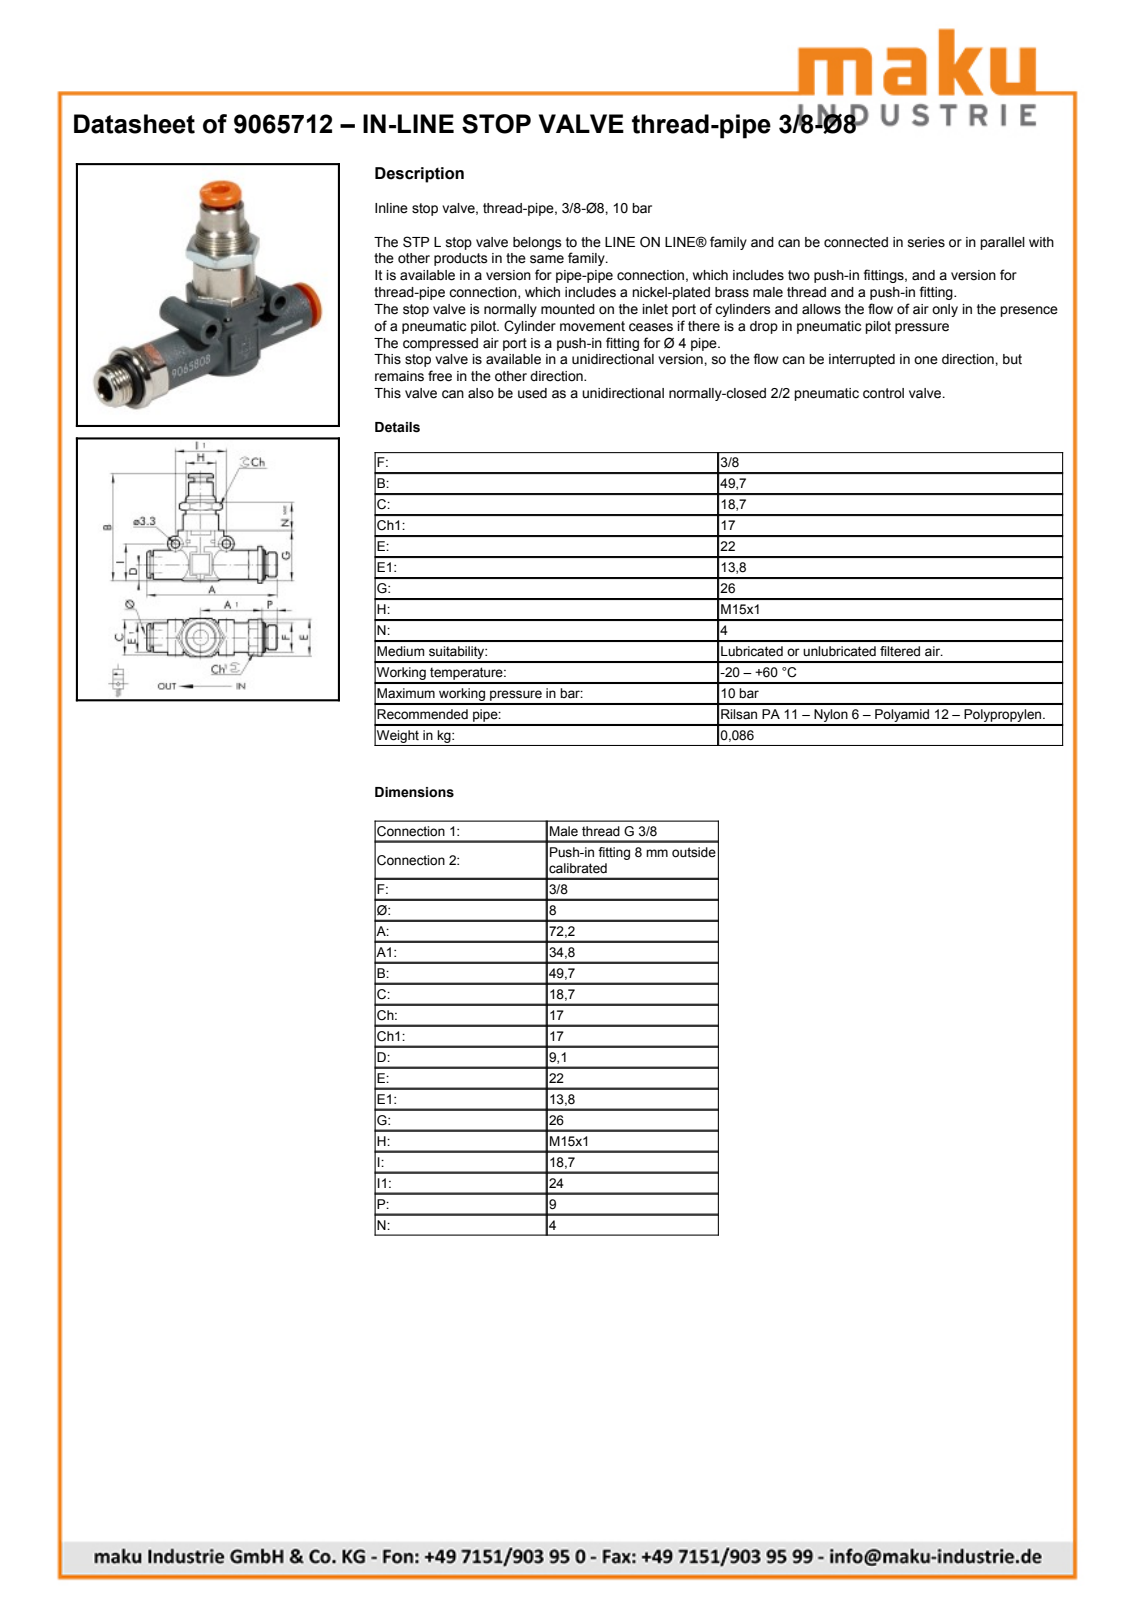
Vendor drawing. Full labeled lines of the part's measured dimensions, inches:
Part name (STEP PRODUCT): 9065712; LINE-ON-LINE D8 PNV_L-body; LINE-ON-LINE D8-3/8 RML-thread port; LINE-ON-LINE D8 VNR-L bushing (+2 more)
STEP written by: PARTsolutions (AUTOMOTIVE_DESIGN)
Units: inches
Bodies: 5 solids, 191 faces (111 planar, 59 cylindrical, 21 other)
Overall size (bounding box): 2.843 × 2.031 × 0.866
Volume: 0.939 in³ · Surface area: 19.11 in²
Round holes (diameter × count): ⌀0.13 ×2, ⌀0.236 ×2, ⌀0.218 ×1, ⌀0.244 ×1, ⌀0.319 ×1, ⌀0.394 ×1, ⌀0.433 ×1, ⌀0.459 ×1, ⌀0.492 ×1, ⌀0.591 ×1
Round bosses / shafts (diameter × count): ⌀0.236 ×2, ⌀0.866 ×1, ⌀0.74 ×1, ⌀0.709 ×1, ⌀0.656 ×1, ⌀0.575 ×1, ⌀0.543 ×1, ⌀0.535 ×1
Partial cylindrical surfaces — rounded edges, fillets, slot ends (radius × count): R0.148 ×1, R0.378 ×1, R0.407 ×1, R0.451 ×1
Main face-to-face distances: 0.949, 0.161, 0.787, 0.386, 0.669, 0.728, 0.807, 1.854, 1.693, 0.906
Hole centre spacings: 0.605, 0.945
